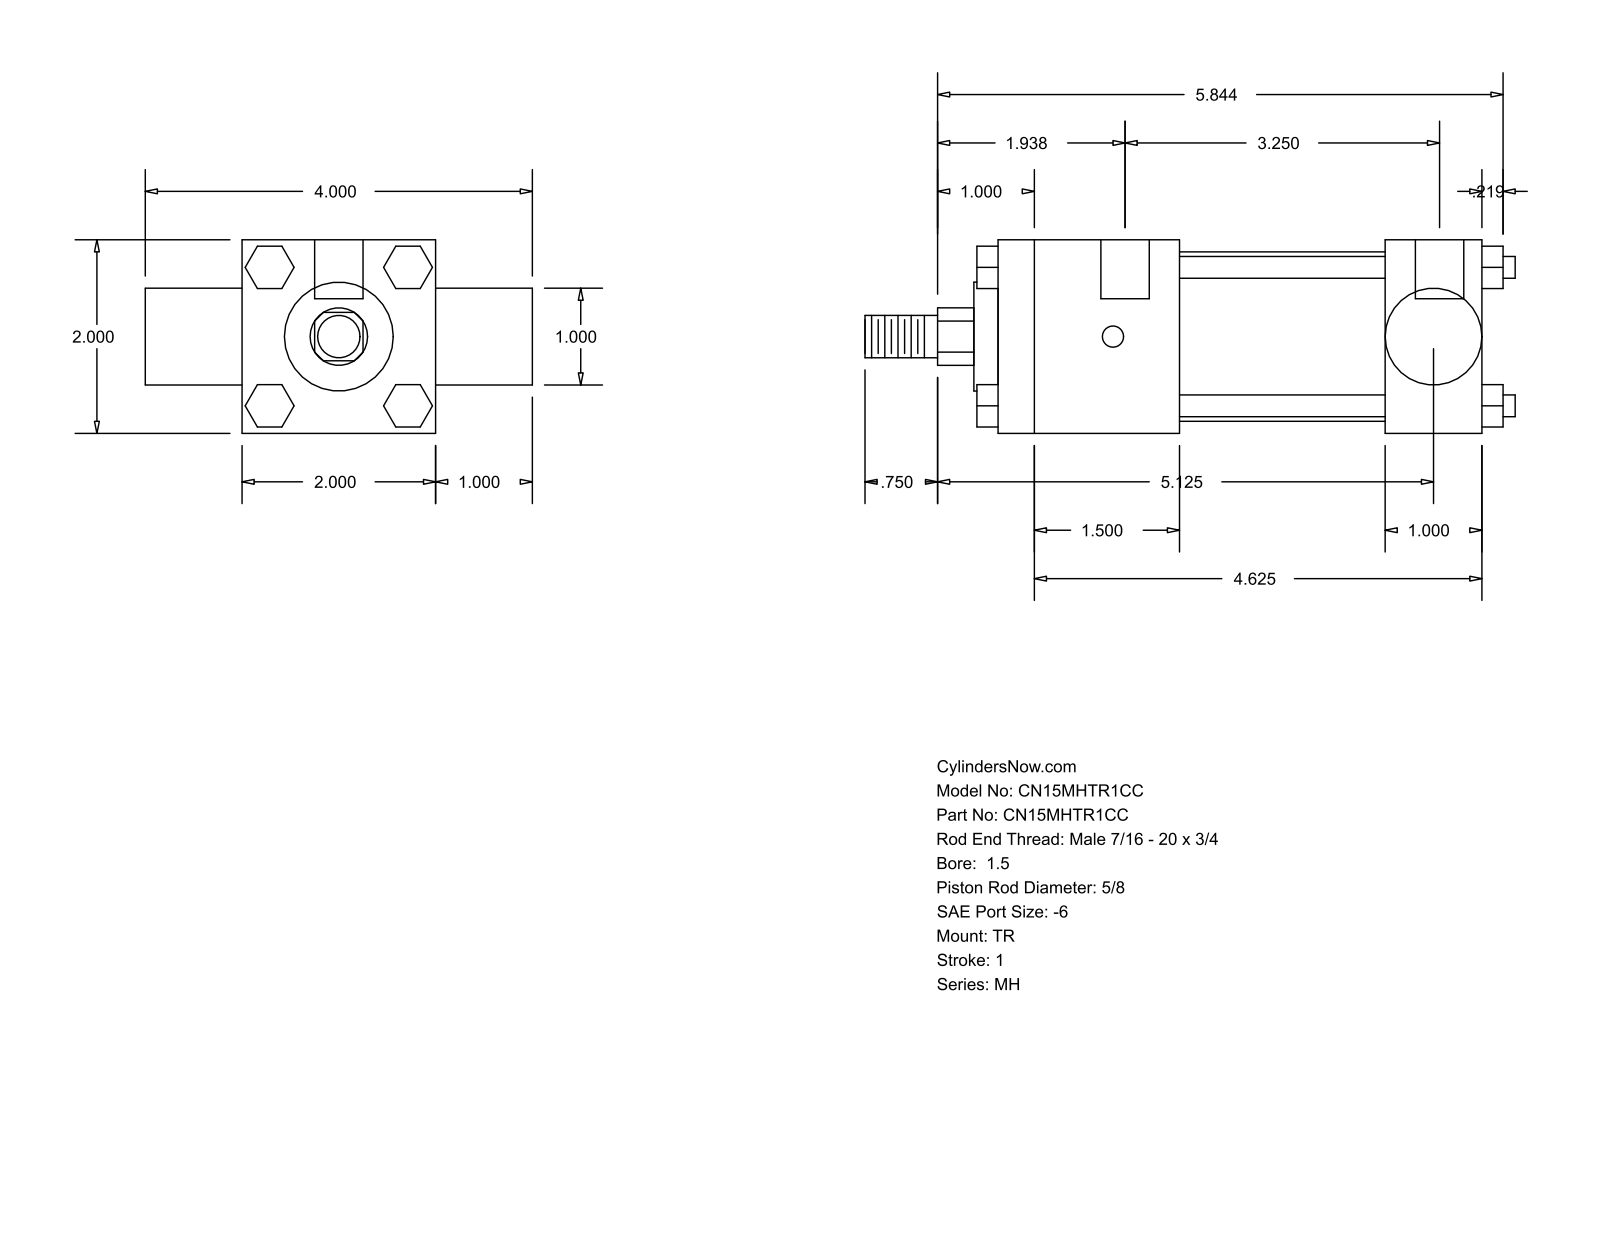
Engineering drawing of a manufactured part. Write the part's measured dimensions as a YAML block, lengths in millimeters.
part_name: "MH_TR__0150_0.625"
step_written_by: "GSSL Pune (CONFIG_CONTROL_DESIGN)"
units: millimeters
bodies: {solids: 0, faces: 120, planar: 92, cylindrical: 28, other: 0}
overall_size: [170.66, 101.6, 50.8]
round_holes:
  - {diameter: 5.56, count: 3}
  - {diameter: 12.7, count: 2}
round_bosses_or_shafts:
  - {diameter: 5.71, count: 4}
  - {diameter: 44.45, count: 1}
  - {diameter: 28.57, count: 1}
  - {diameter: 25.35, count: 1}
  - {diameter: 15.88, count: 1}
  - {diameter: 11.11, count: 1}
partial_cylinders:
  - {radius: 7.54, count: 1}
face_to_face_distances: [50.8, 127, 53.97, 25.4, 76.2, 47.62, 79.38, 101.59, 25.41, 11.11]
hole_center_spacings: [3.17, 82.55, 85.72]
